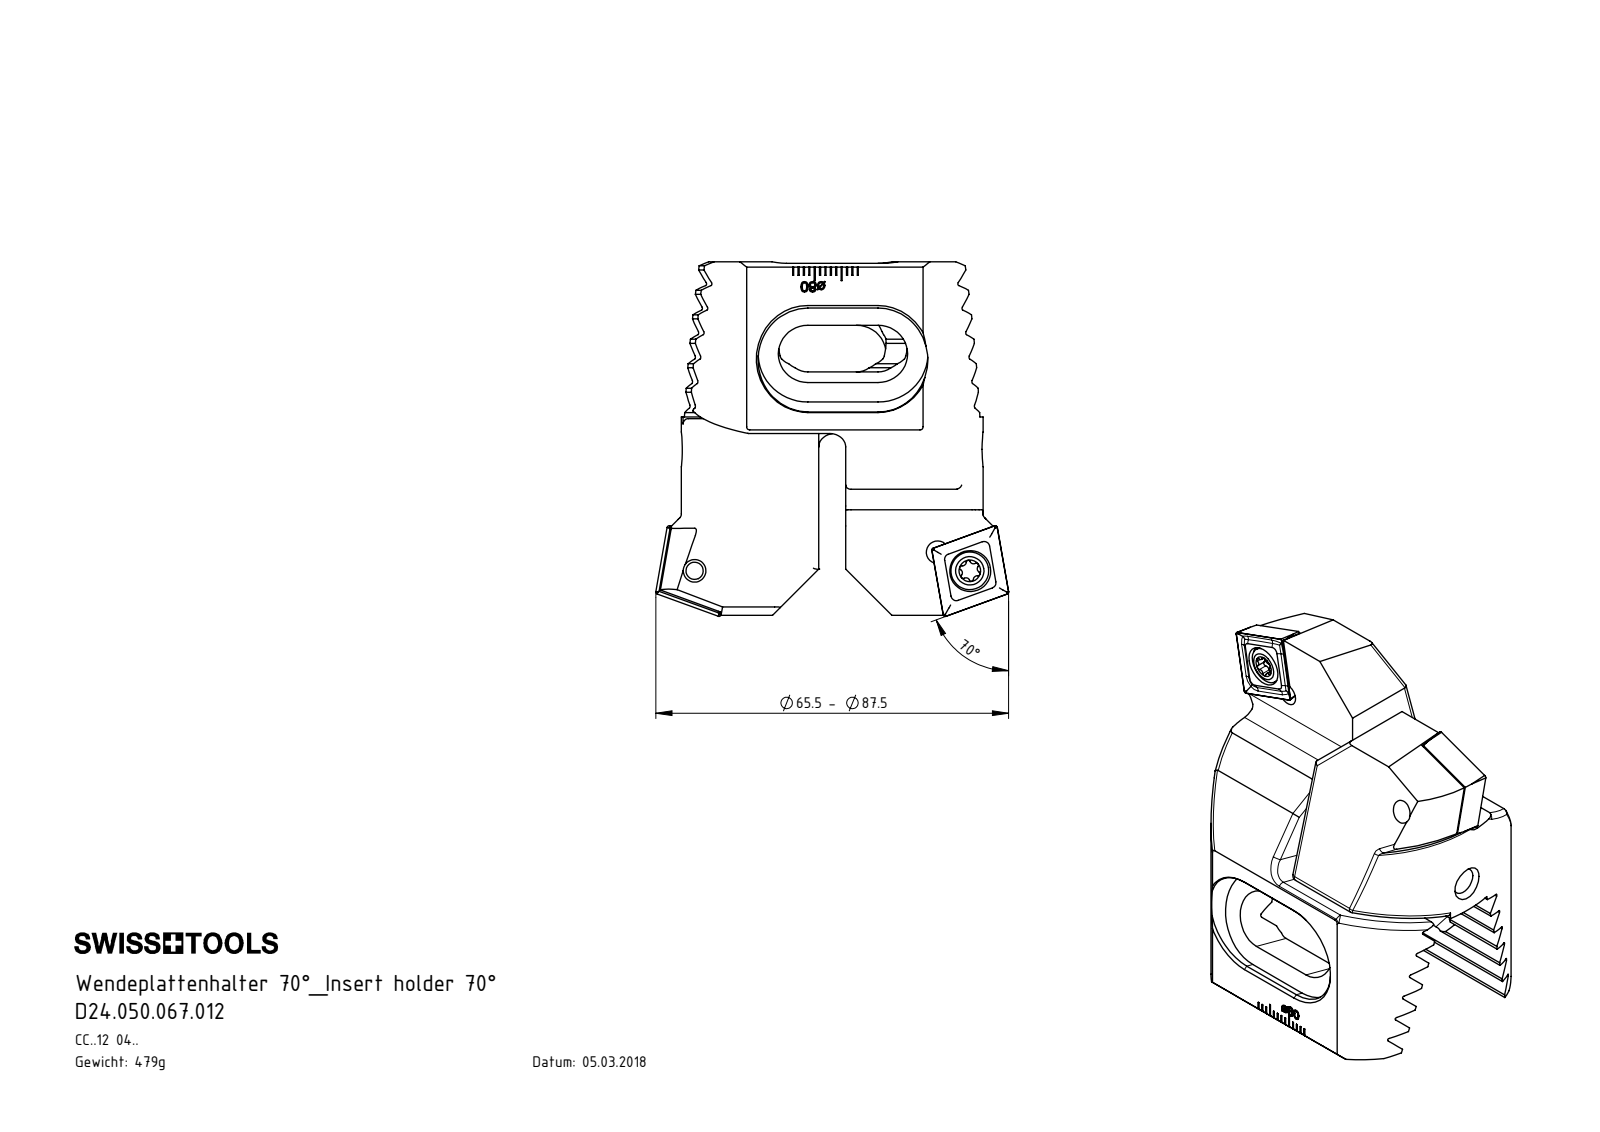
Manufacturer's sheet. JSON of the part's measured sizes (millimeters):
{"part_name": "Z55-xxx.001.037_C_CC 12 70ø; D24.050.067.012; WCC-ER2.001.010_A; CCMT120404 (+1 more)", "step_written_by": "SolidWorks 2017 (CONFIG_CONTROL_DESIGN)", "units": "millimeters", "bodies": {"solids": 8, "faces": 692, "planar": 336, "cylindrical": 132, "other": 224}, "overall_size": [65.8, 65.5, 44.2], "volume_mm3": 61870, "surface_area_mm2": 22753, "round_holes": [[4.2, 4], [2, 2], [5.5, 2], [7.6, 2], [5, 1]], "round_bosses_or_shafts": [[7, 2], [5, 2], [6, 1], [4, 1]], "partial_cylinders_radius": [[1, 14], [0.34, 12], [0.39, 12], [0.69, 8], [3, 6], [0.69, 4], [5.5, 4], [9.25, 4]], "face_to_face_distances": [4.07, 8.14, 12.21, 16.28, 20.35, 7.85, 1.69, 21.8, 22.4, 5], "hole_center_spacings": [6.89, 6.98, 16, 45.25, 45.33, 51.16, 30.9, 39.16]}
